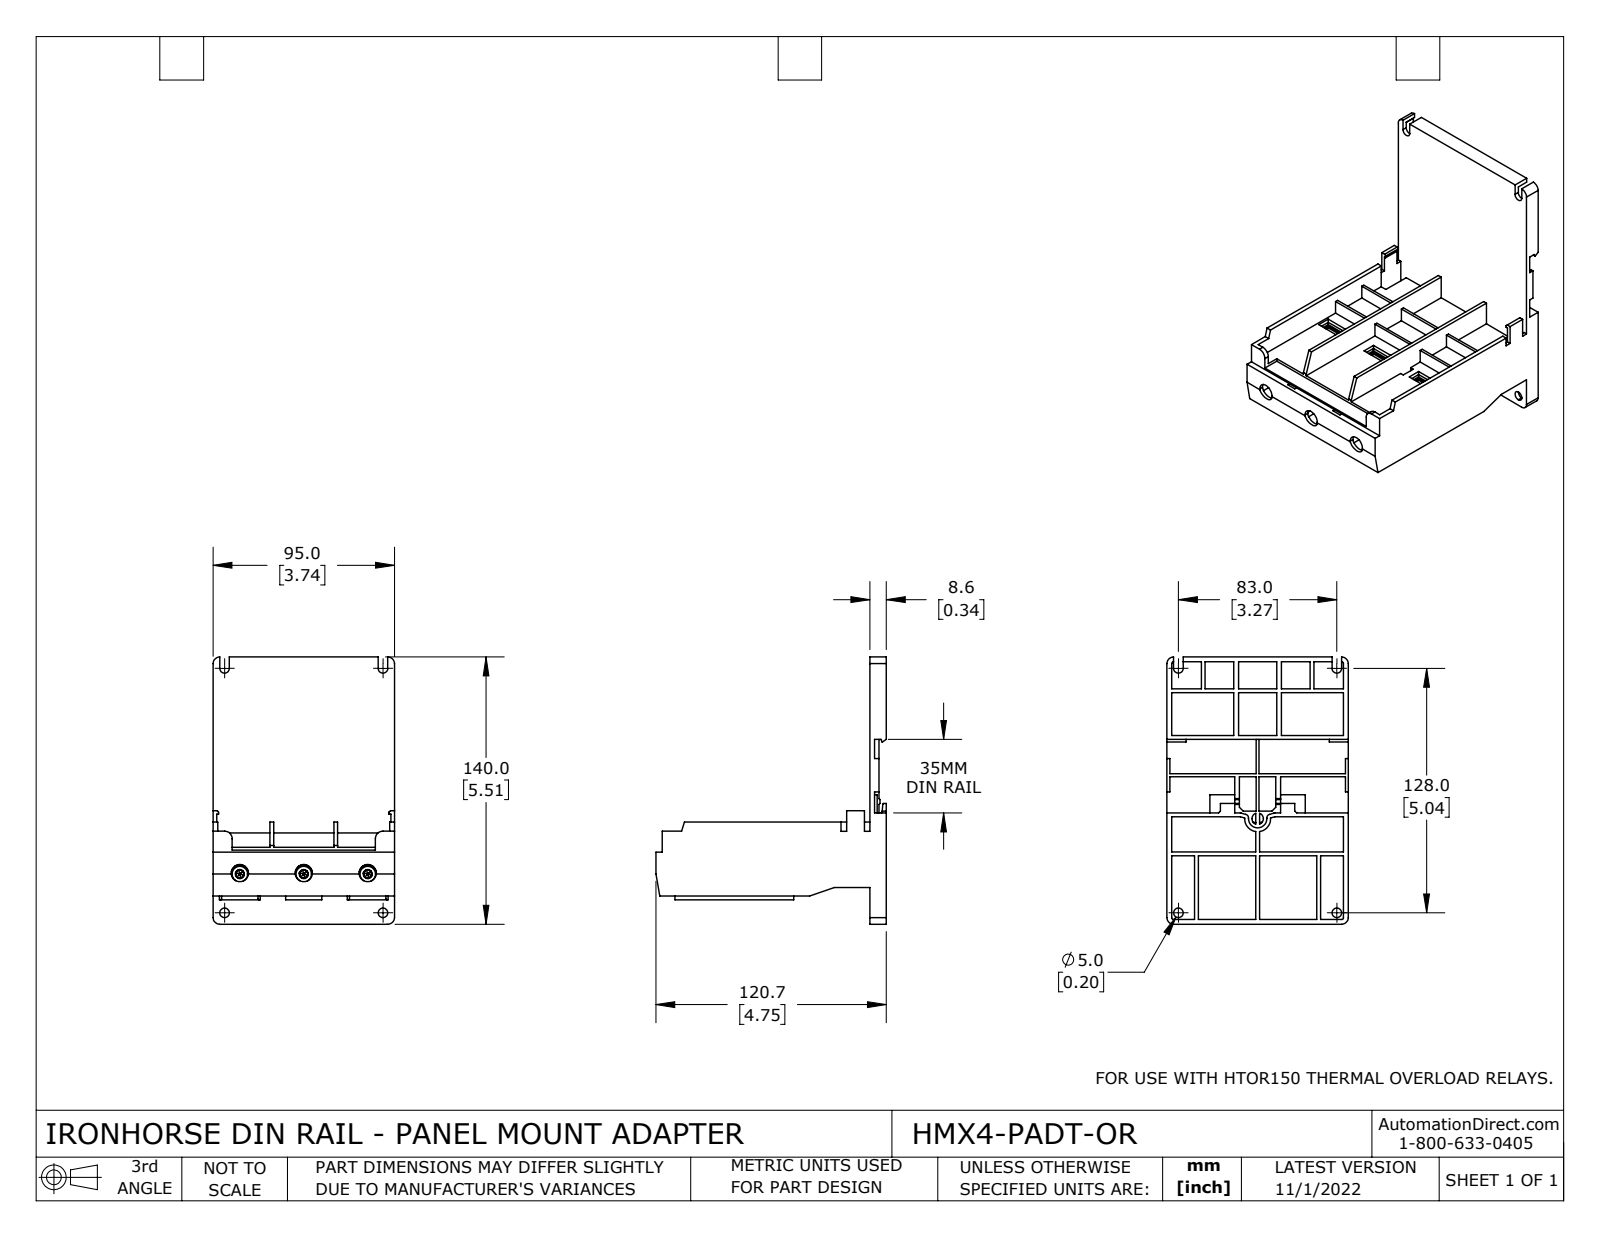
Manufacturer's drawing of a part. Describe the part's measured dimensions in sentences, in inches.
The part is named "HMX4-PADT-OR". Its 3-D file was written by "SolidWorks 2021 (CONFIG_CONTROL_DESIGN)". It is 7 solids with 1505 faces: 1040 planar, 327 cylindrical and 138 other. Overall it measures 5.512 by 4.752 by 3.74 inches. Its volume is 10.13 cubic inches and its surface area 222.2 square inches. Round holes: 3 of diameter 0.102, 3 of diameter 0.118, 3 of diameter 0.165, 3 of diameter 0.173, 3 of diameter 0.354, 2 of diameter 0.197. Round bosses or shafts: 3 of diameter 0.362, 3 of diameter 0.319, 3 of diameter 0.244. Partial cylindrical surfaces (rounded edges, fillets, slot ends): 32 of radius 0.014, 24 of radius 0.012, 22 of radius 0.02, 20 of radius 0.098, 16 of radius 0.039, 7 of radius 0.118, 6 of radius 0.016, 4 of radius 0.024. The main face-to-face distances are 0.079, 0.098, 1.319, 0.094, 0.827, 1.171, 0.925, 2.49, 0.065, 0.144. The hole center spacings are 1.319, 2.638, 0.02, 0.859, 0.878, 1.819, 1.828, 3.059.
